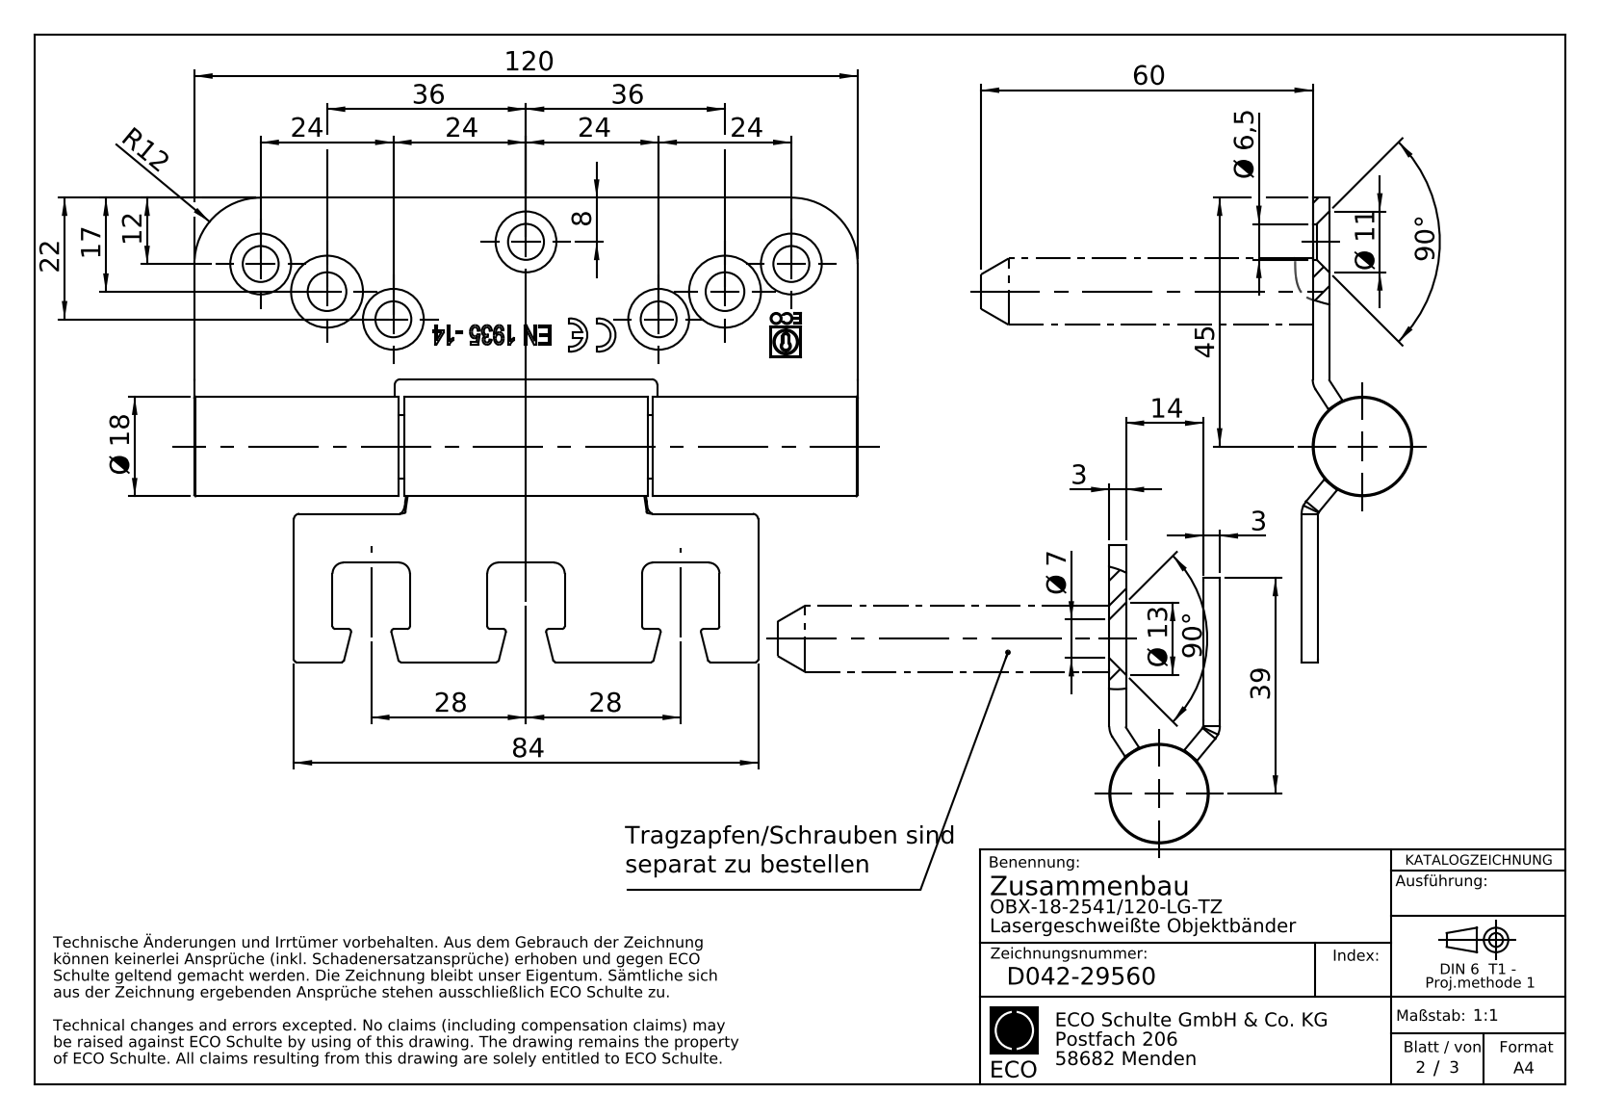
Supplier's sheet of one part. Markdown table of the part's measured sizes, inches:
| quantity | value |
| --- | --- |
| part name | B01572; D043-24263; ISO 10642; DIN5401-III (+7 more) |
| STEP written by | SolidWorks 2017 (AUTOMOTIVE_DESIGN) |
| units | inches |
| bodies | 15 solids, 533 faces (242 planar, 159 cylindrical, 132 other) |
| overall size | 4.724 × 3.15 × 2.126 |
| volume | 3.665 in³ |
| surface area | 54.54 in² |
| round holes (diameter × count) | 0.256 × 5, 0.079 × 2, 0.197 × 2, 0.02 × 1, 0.177 × 1, 0.311 × 1 |
| round bosses / shafts (diameter × count) | 0.472 × 3, 0.236 × 2, 0.709 × 1, 0.465 × 1, 0.453 × 1, 0.303 × 1, 0.157 × 1, 0.065 × 1 |
| partial cylindrical surfaces (radius × count) | 0.02 × 22, 0.01 × 6, 0.079 × 6, 0.039 × 4, 0.027 × 2, 0.083 × 2, 0.118 × 2, 0.138 × 2 |
| main face-to-face distances | 0.118, 0.669, 0.787, 0.551, 3.228, 0.453, 4.272, 4.724, 0.039, 0.472 |
| hole center spacings | 0.512, 1.024, 1.094, 1.461, 1.896, 2.37, 2.862, 3.313 |
